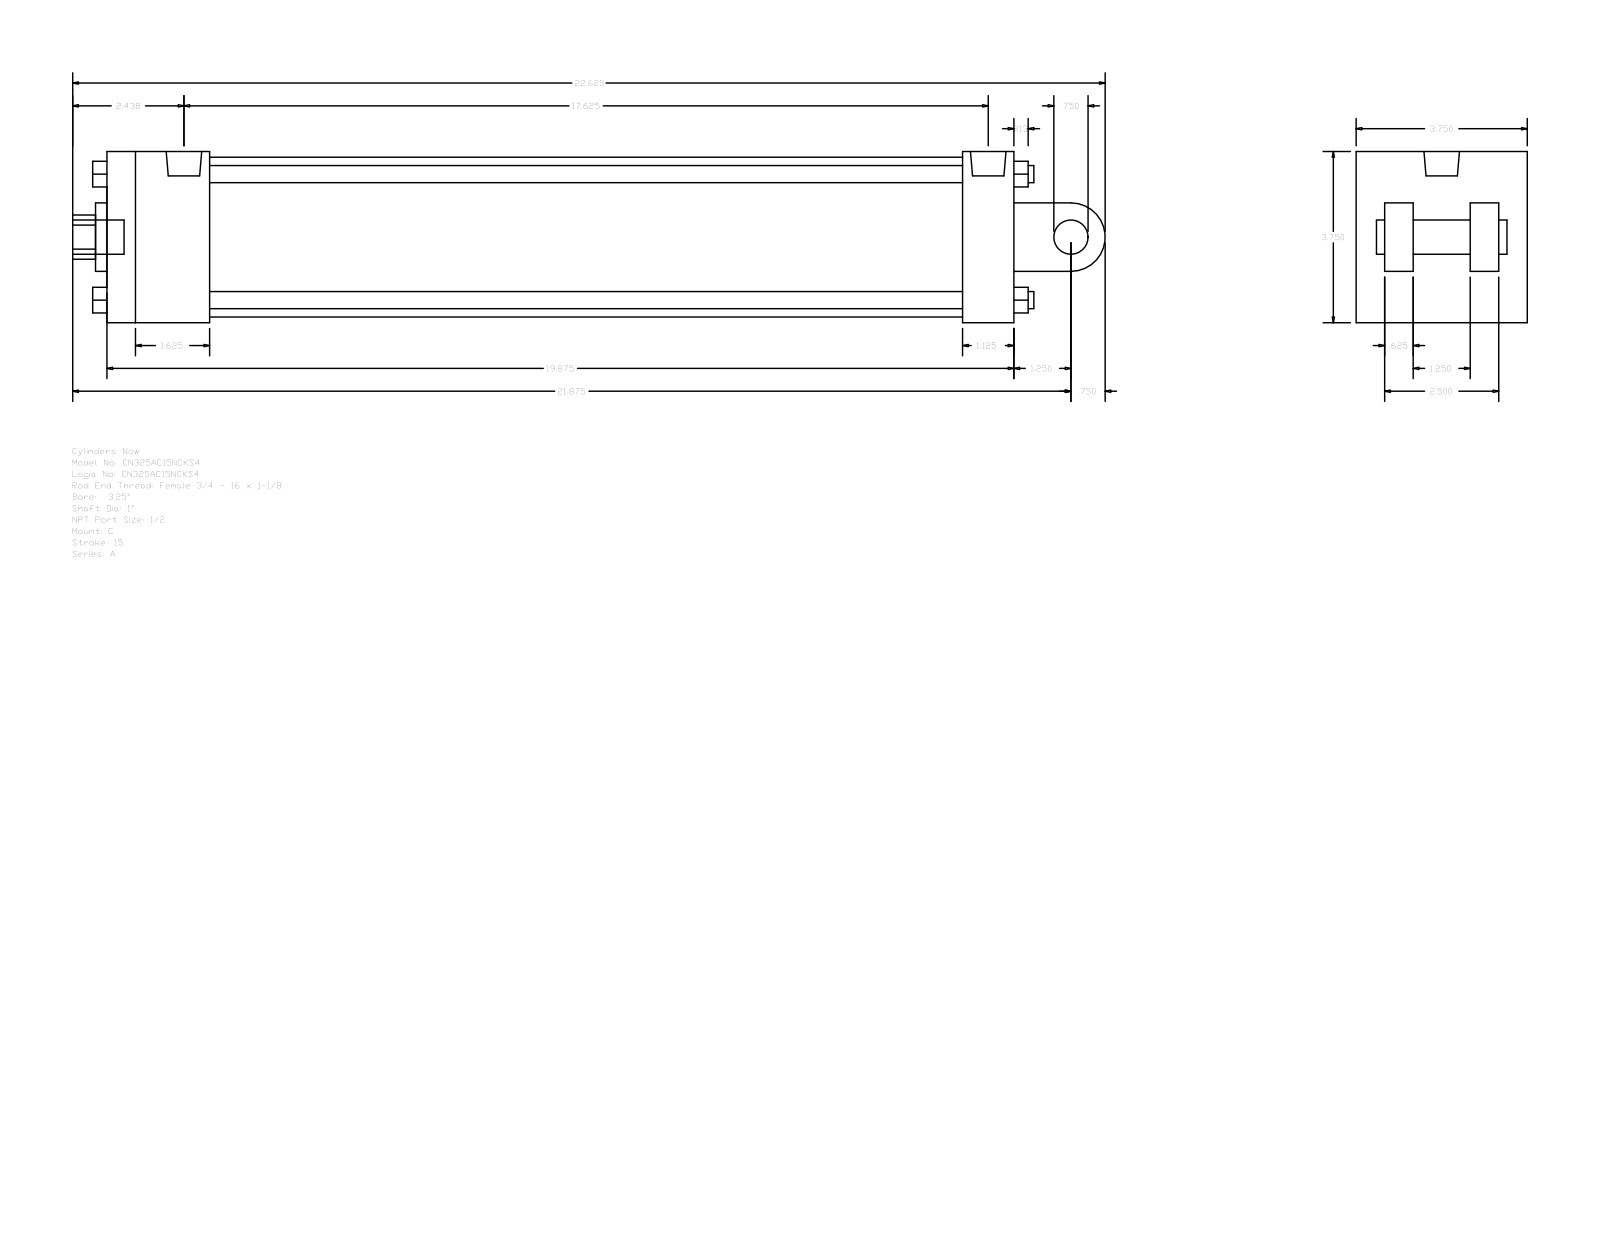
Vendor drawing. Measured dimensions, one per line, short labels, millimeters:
name: A_C__0325_1
written by: GSSL Pune (CONFIG_CONTROL_DESIGN)
unit: mm
bodies: 0 solids, 135 faces (102 planar, 33 cylindrical, 0 other)
size: 574.67 × 95.25 × 95.25
holes: 2× ⌀8.73, 1× ⌀19.77, 1× ⌀25.4, 1× ⌀38.1, 1× ⌀88.9
bosses: 4× ⌀9.53, 2× ⌀19.05, 2× ⌀8.73, 1× ⌀19.77
rounds: 1× R12.29, 1× R19.05
face distances: 95.24, 504.83, 15.87, 63.5, 47.63, 31.74, 79.37, 66.67, 476.25, 28.58
hole spacings: 3.18
